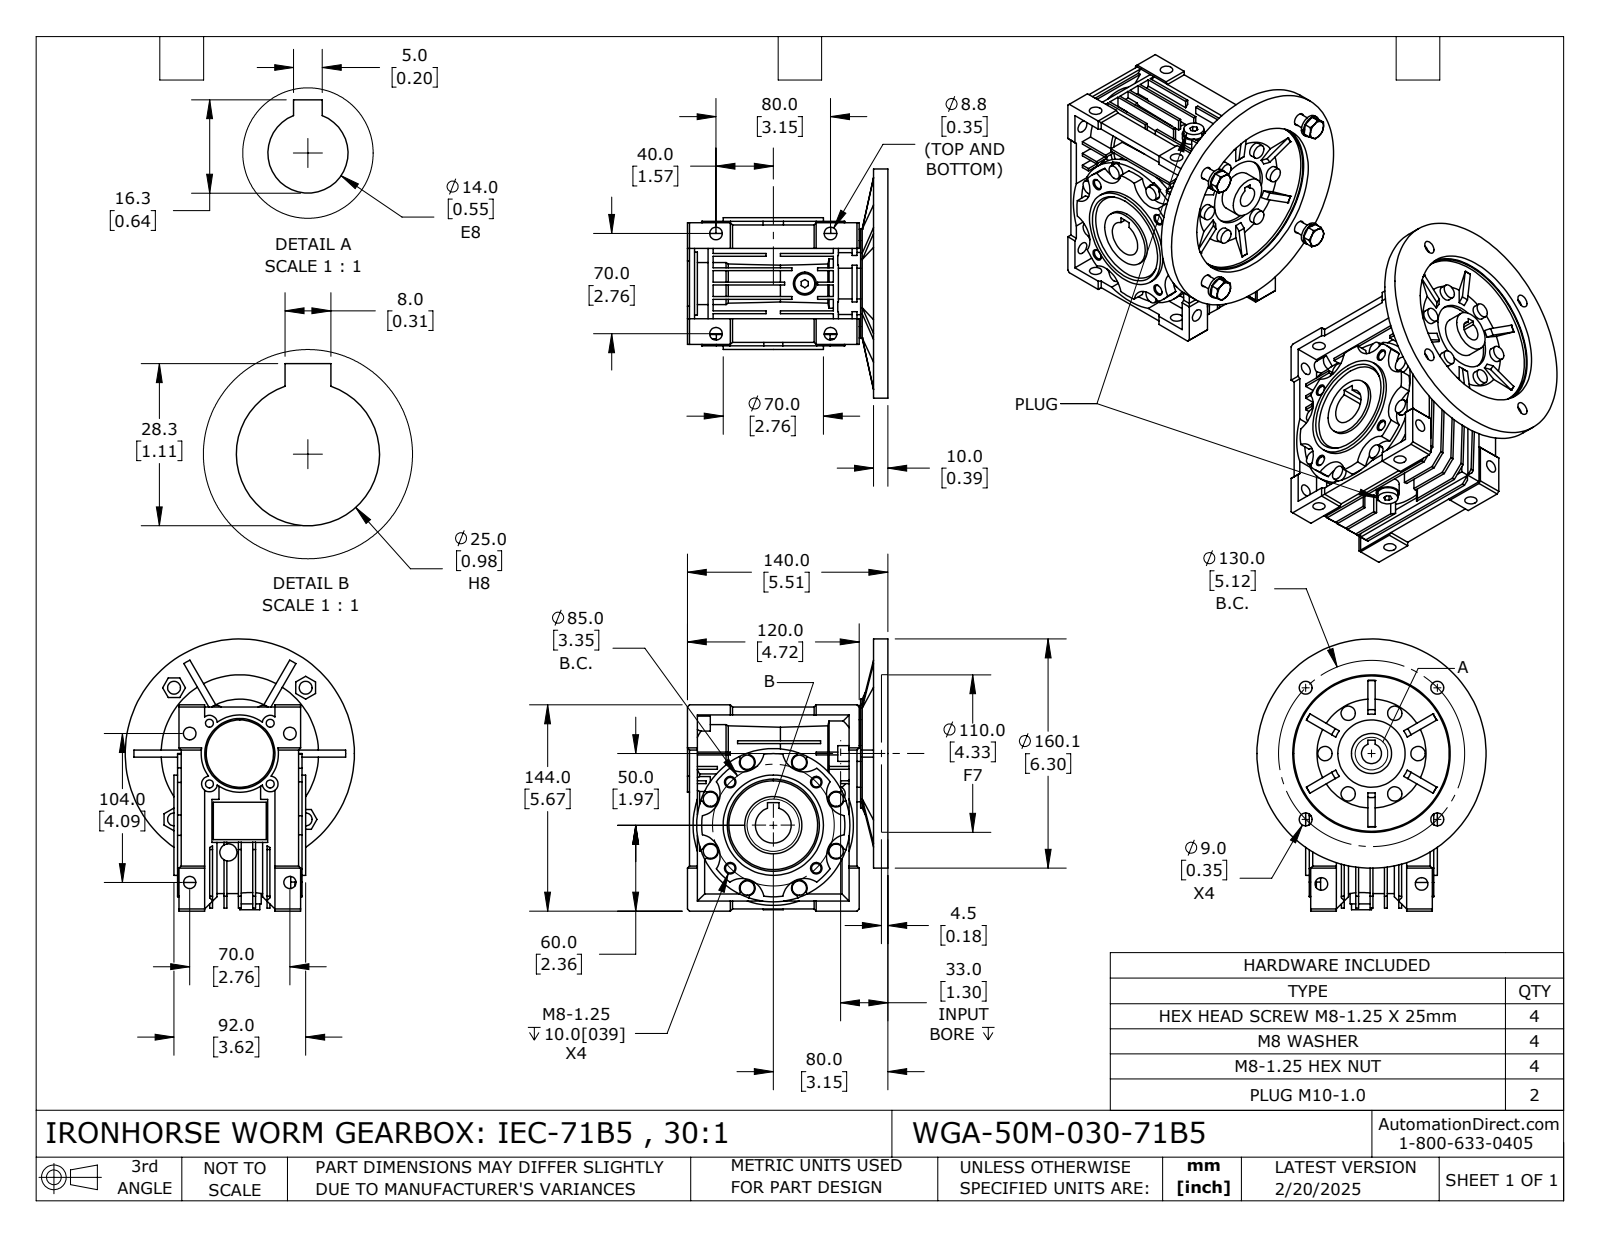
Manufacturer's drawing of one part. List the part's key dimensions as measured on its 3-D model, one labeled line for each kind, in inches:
Part name (STEP PRODUCT): WGA-50M-030-71B5
STEP written by: SolidWorks 2024 (CONFIG_CONTROL_DESIGN)
Units: inches
Bodies: 7 solids, 1007 faces (577 planar, 316 cylindrical, 114 other)
Overall size (bounding box): 7.481 × 6.302 × 5.512
Volume: 69.93 in³ · Surface area: 397.8 in²
Round holes (diameter × count): ⌀0.346 ×8, ⌀0.335 ×6, ⌀0.354 ×6, ⌀0.219 ×4, ⌀0.262 ×2, ⌀0.262 ×2, ⌀0.551 ×1, ⌀0.591 ×1, ⌀0.984 ×1, ⌀1.102 ×1, ⌀1.339 ×1, ⌀1.575 ×1
Round bosses / shafts (diameter × count): ⌀0.394 ×14, ⌀0.63 ×2, ⌀0.551 ×2, ⌀0.386 ×2, ⌀0.327 ×2, ⌀6.302 ×1, ⌀4.213 ×1, ⌀2.992 ×1
Partial cylindrical surfaces — rounded edges, fillets, slot ends (radius × count): R0.217 ×18, R0.236 ×8, R0.591 ×8, R0.61 ×8, R0.817 ×1, R1.811 ×1, R1.878 ×1, R1.969 ×1
Main face-to-face distances: 0.394, 0.079, 0.276, 0.217, 0.315, 0.059, 0.787, 0.197, 2.165, 1.378
Hole centre spacings: 2.818, 2.756, 1.181, 1.378, 1.67, 1.673, 2.366, 2.559
